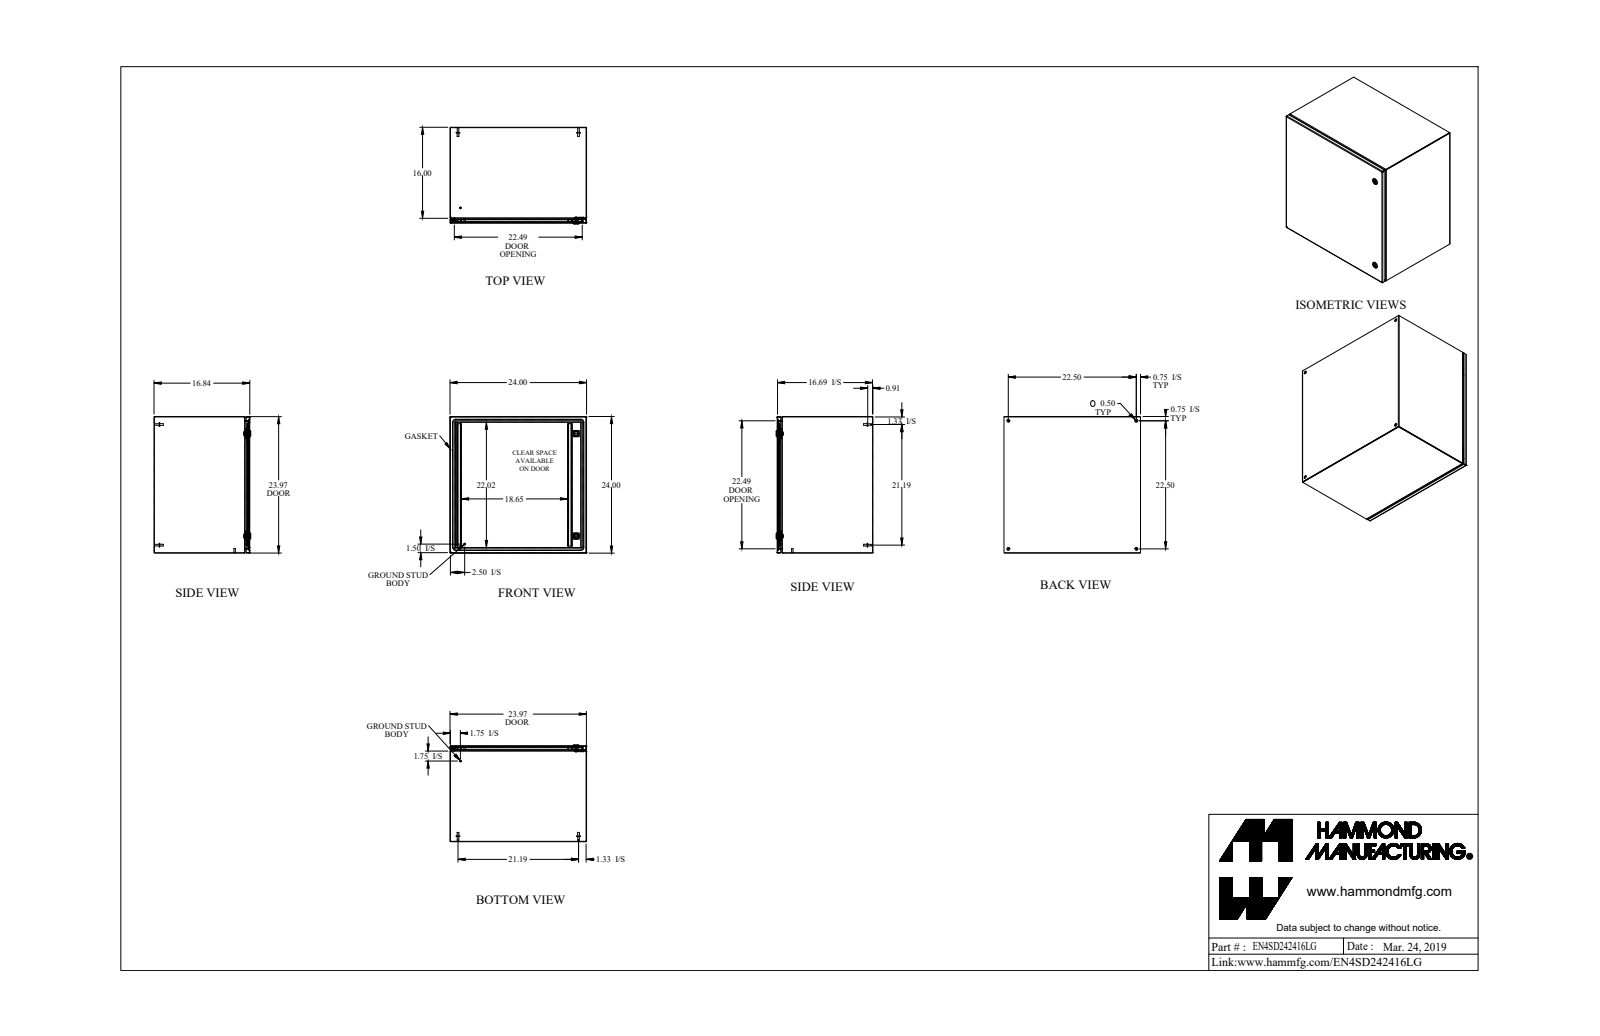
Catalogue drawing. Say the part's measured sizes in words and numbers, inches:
The part is named "EN4SD242416LG". Its 3-D file was written by "SolidWorks 2019 (AUTOMOTIVE_DESIGN)". It is 29 solids with 736 faces: 363 planar, 245 cylindrical and 128 other. Overall it measures 24 by 24 by 16.997 inches. Its volume is 218.8 cubic inches and its surface area 6 126 square inches. Round holes: 4 of diameter 0.5, 2 of diameter 0.232, 2 of diameter 0.625, 2 of diameter 0.785, 1 of diameter 0.172, 1 of diameter 0.24, 1 of diameter 0.242. Round bosses or shafts: 4 of diameter 0.625, 4 of diameter 0.313, 4 of diameter 0.27, 2 of diameter 1.1, 2 of diameter 0.525, 2 of diameter 0.281, 2 of diameter 0.25, 1 of diameter 0.455. Partial cylindrical surfaces (rounded edges, fillets, slot ends): 14 of radius 0.036, 14 of radius 0.108, 12 of radius 0.043, 12 of radius 0.081, 12 of radius 0.312, 8 of radius 0.1, 4 of radius 0.006, 4 of radius 0.062. The main face-to-face distances are 0.072, 23.928, 16.765, 23.856, 24, 16.693, 16.837, 0.837, 15.928, 0.75. The hole center spacings are 22.5, 31.82, 2.493, 2.494, 17.999, 20.277, 20.278, 21.544.
